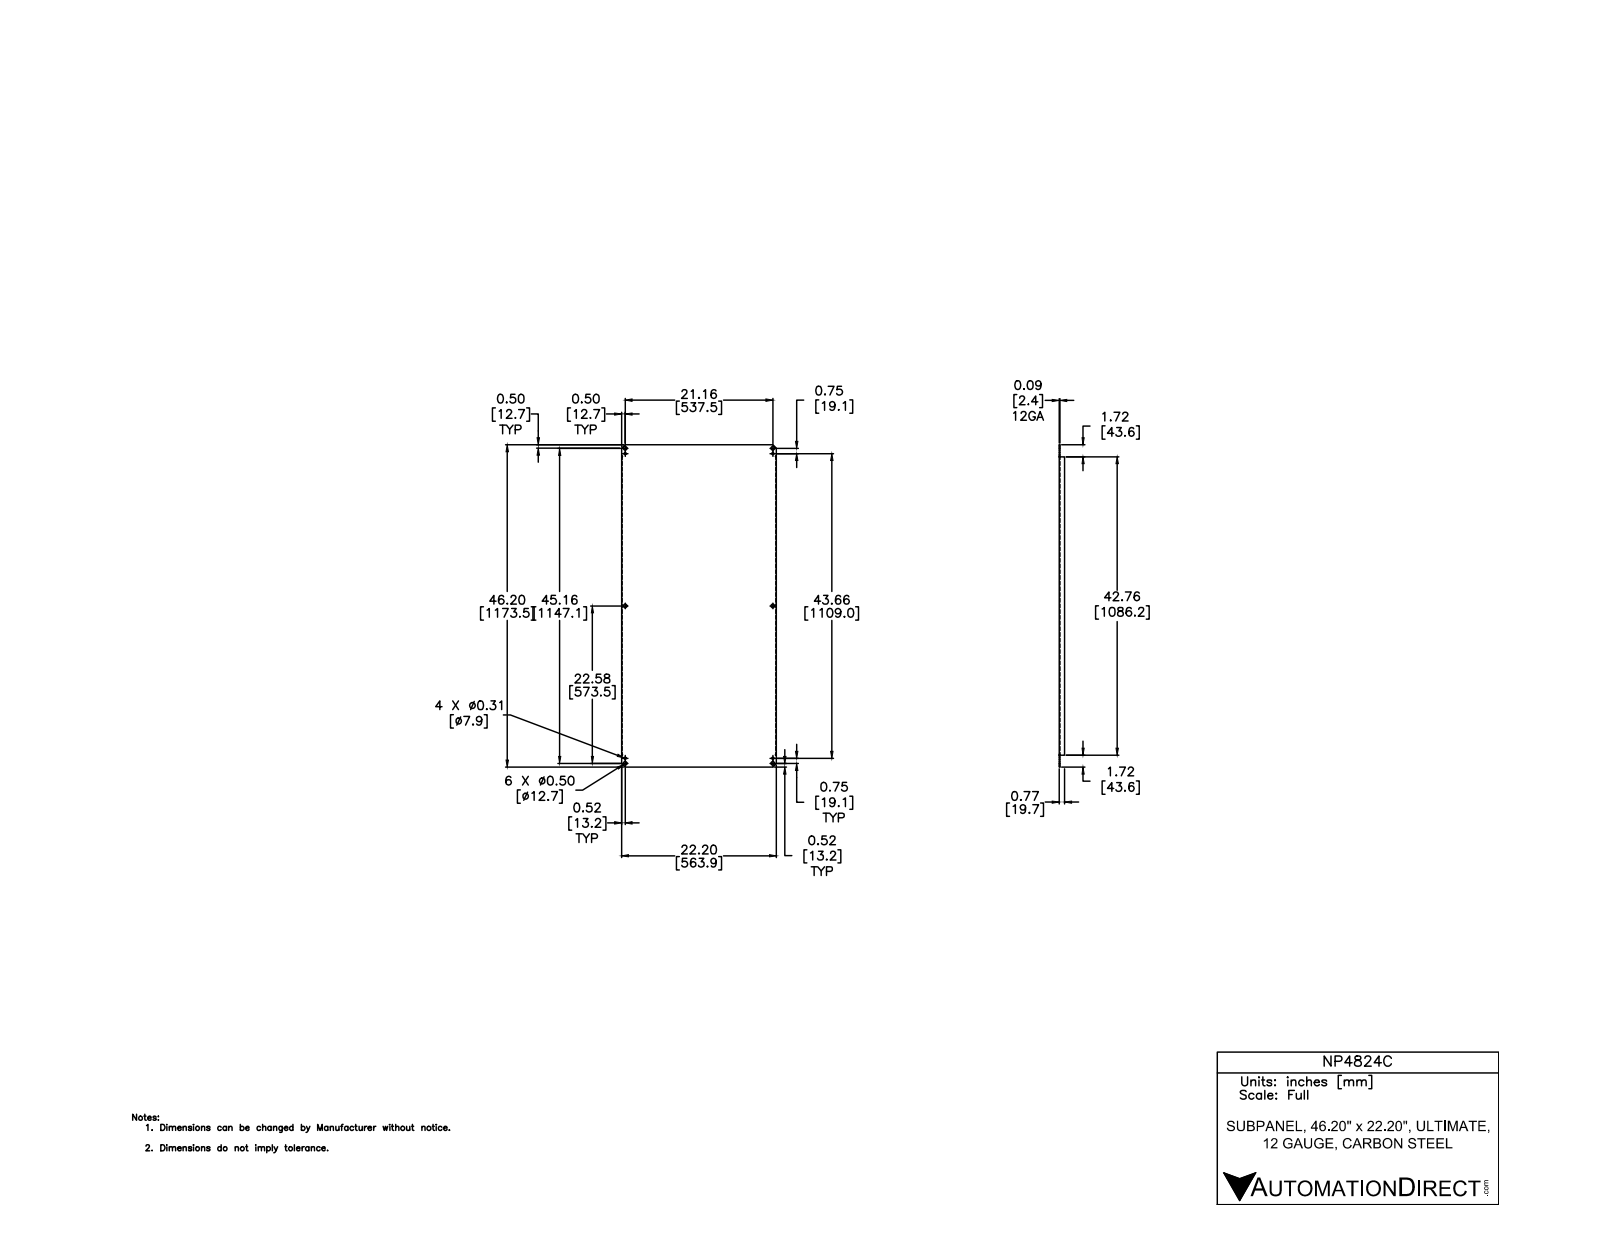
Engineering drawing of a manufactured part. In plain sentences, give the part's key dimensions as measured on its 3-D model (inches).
The part is named "NP4824C". Its 3-D file was written by "Autodesk Inventor 2012 (AUTOMOTIVE_DESIGN)". It is 1 solid with 44 faces: 30 planar, 14 cylindrical and 0 other. Overall it measures 46.2 by 22.2 by 0.774 inches. Its volume is 101.2 cubic inches and its surface area 2 173 square inches. Round holes: 6 of diameter 0.5, 4 of diameter 0.313. Partial cylindrical surfaces (rounded edges, fillets, slot ends): 2 of radius 0.016, 2 of radius 0.109. The main face-to-face distances are 0.094, 22.106, 22.2, 22.013, 0.68, 0.774, 46.2, 1.718, 44.482, 42.764. The hole center spacings are 21.16, 0.75, 21.173, 21.83, 22.58, 30.402, 30.945, 44.41.
